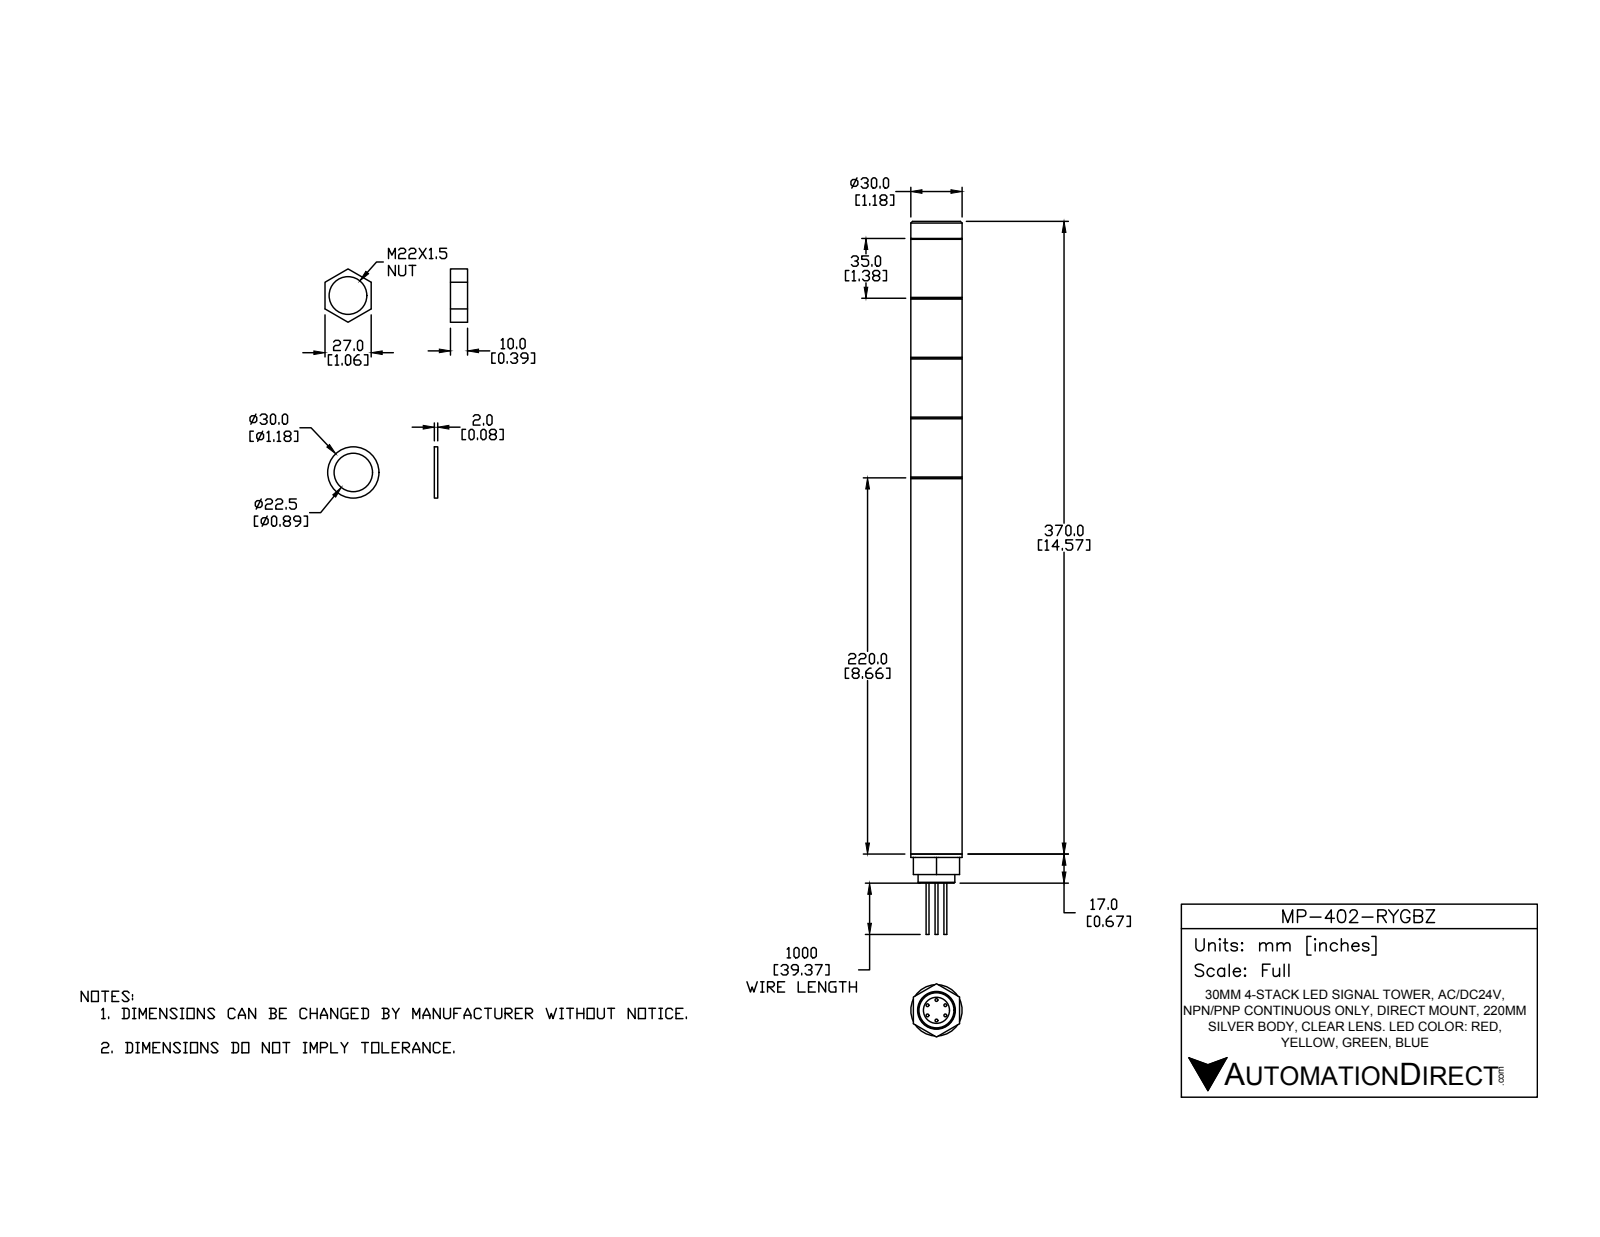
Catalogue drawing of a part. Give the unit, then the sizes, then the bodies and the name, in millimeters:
Units: millimetres
Overall size (bounding box): 417 × 31.18 × 30
Round holes (diameter × count): ⌀3.2 ×1, ⌀7.7 ×1, ⌀15.3 ×1, ⌀20.7 ×1, ⌀22 ×1
Round bosses / shafts (diameter × count): ⌀1.7 ×6, ⌀30 ×1, ⌀21.5 ×1, ⌀5 ×1
Main face-to-face distances: 35, 70, 105, 140, 222, 257, 292, 327, 45, 372
Volume: 257 464 mm³ · Surface area: 53 403 mm²
Bodies: 15 solids, 119 faces (53 planar, 42 cylindrical, 24 other)
Part name (STEP PRODUCT): MP-402-RYGBZ
STEP written by: SolidWorks 2016 (AUTOMOTIVE_DESIGN)
